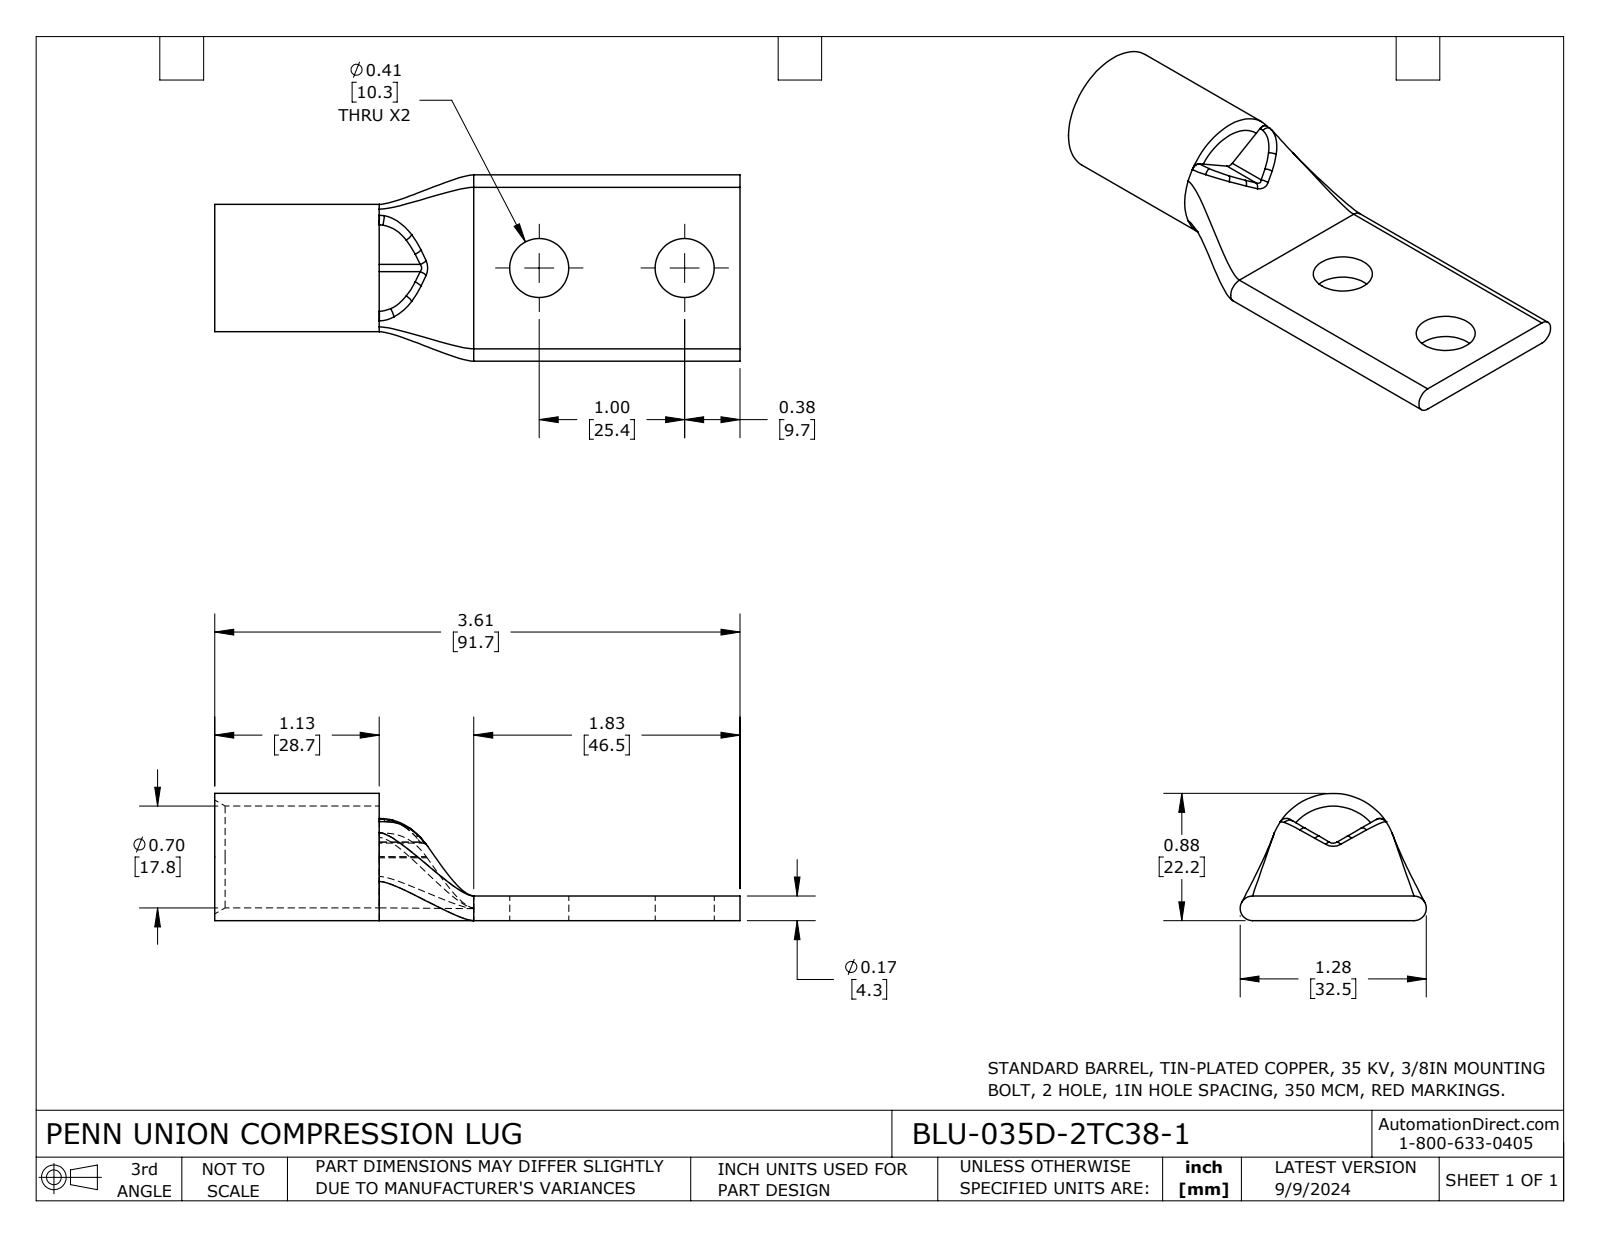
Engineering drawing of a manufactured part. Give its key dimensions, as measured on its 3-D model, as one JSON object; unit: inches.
{"part_name": "BLU-035D-2TC38-1", "step_written_by": "SolidWorks 2023 (CONFIG_CONTROL_DESIGN)", "units": "inches", "bodies": {"solids": 1, "faces": 45, "planar": 11, "cylindrical": 13, "other": 21}, "overall_size": [3.61, 1.28, 0.875], "volume_in3": 0.715, "surface_area_in2": 14.58, "round_holes": [[0.406, 2], [0.7, 1]], "round_bosses_or_shafts": [[0.875, 1]], "partial_cylinders_radius": [[0.05, 2], [0.085, 2]], "face_to_face_distances": [0.17, 0.087, 3.61, 1.13, 2.48, 1.78, 0.65, 1.83], "hole_center_spacings": [1]}
